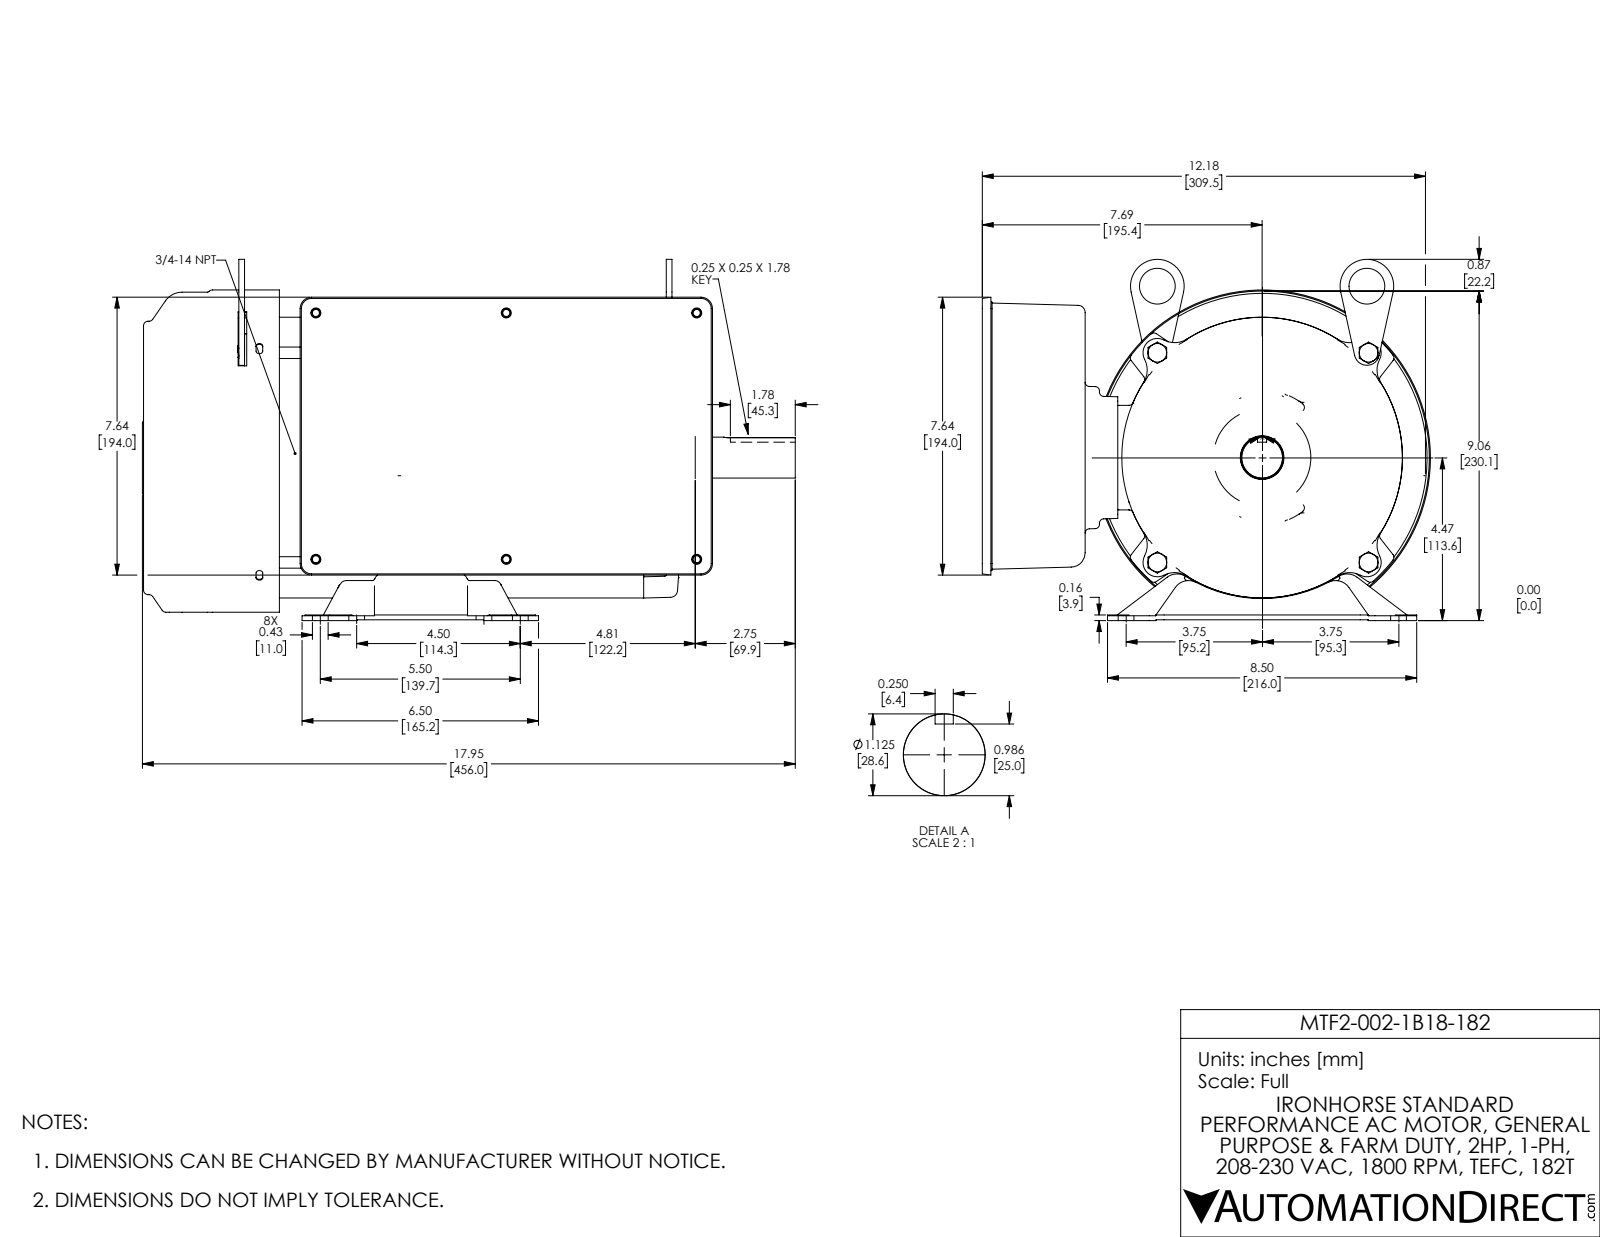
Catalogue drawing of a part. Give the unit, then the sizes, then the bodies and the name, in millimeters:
Units: millimetres
Overall size (bounding box): 456 × 313 × 252.2
Round holes (diameter × count): ⌀5 ×12, ⌀7 ×8, ⌀11 ×8, ⌀6 ×6, ⌀9.4 ×5, ⌀4.2 ×4, ⌀7.1 ×4, ⌀9.3 ×4, ⌀25 ×2, ⌀19 ×1, ⌀19.6 ×1, ⌀24 ×1
Round bosses / shafts (diameter × count): ⌀11.3 ×4, ⌀8 ×4, ⌀6.7 ×4, ⌀234.6 ×1, ⌀231.4 ×1, ⌀196 ×1, ⌀190.9 ×1, ⌀40 ×1
Partial cylindrical surfaces — rounded edges, fillets, slot ends (radius × count): R1.5 ×53, R5 ×51, R1 ×45, R3 ×42, R2 ×18, R4 ×17, R0.5 ×10, R3.2 ×9
Main face-to-face distances: 1, 4, 71.8, 66.8, 67.8, 70.8, 0.8, 5, 56, 56.8
Hole centre spacings: 147.5, 147, 0.6, 25.4, 50, 69.1, 69.5, 97.7
Volume: 2 607 000 mm³ · Surface area: 1 283 000 mm²
Bodies: 23 solids, 3304 faces (1074 planar, 905 cylindrical, 1325 other)
Part name (STEP PRODUCT): MTF2-002-1B18-182
STEP written by: SolidWorks 2017 (AUTOMOTIVE_DESIGN)
